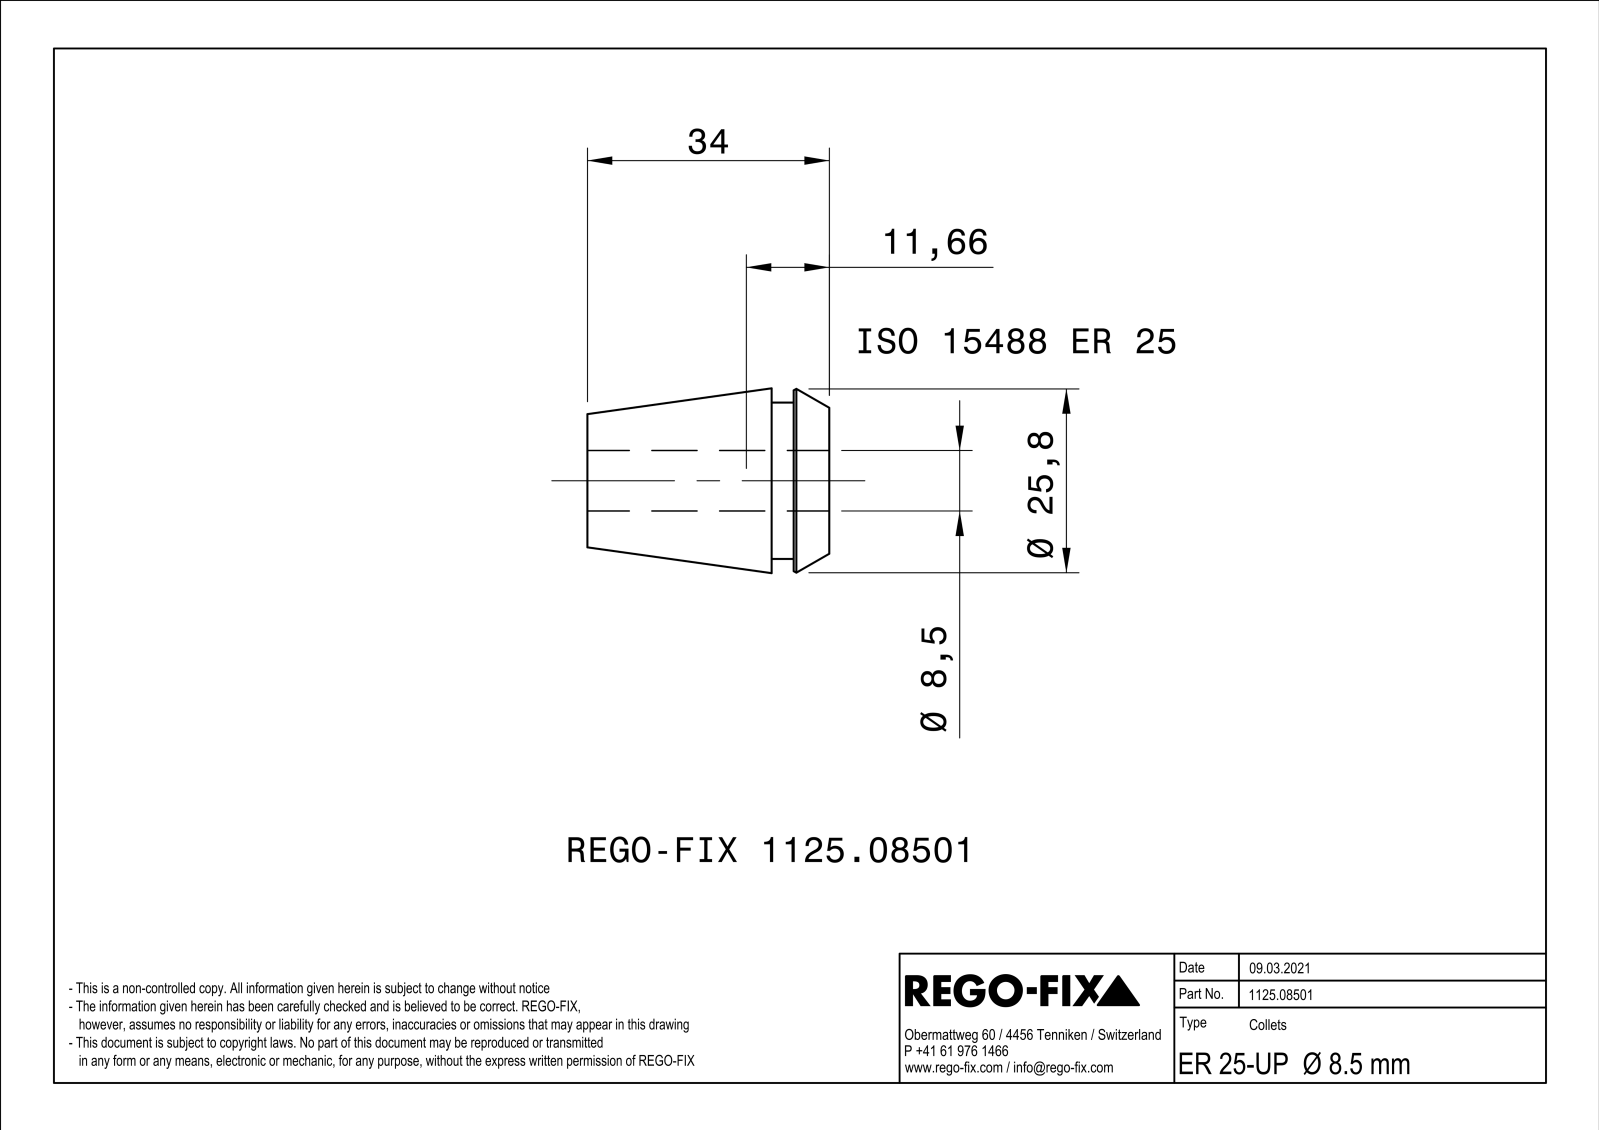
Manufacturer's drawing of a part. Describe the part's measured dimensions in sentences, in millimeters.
The part is named "NOCUT". Its 3-D file was written by "SIEMENS PLM Software Solid Edge ST10 (AUTOMOTIVE_DESIGN)". It is 1 solid with 177 faces: 72 planar, 25 cylindrical and 80 other. Overall it measures 34 by 25.99 by 25.99 millimeters. Its volume is 8 992 cubic millimeters and its surface area 10 014 square millimeters. Round holes: 1 of diameter 8.5. Round bosses or shafts: 1 of diameter 22. Partial cylindrical surfaces (rounded edges, fillets, slot ends): 8 of radius 0.4. The main face-to-face distances are 0.8, 34, 8.1, 25.9, 5, 3.1, 29.
